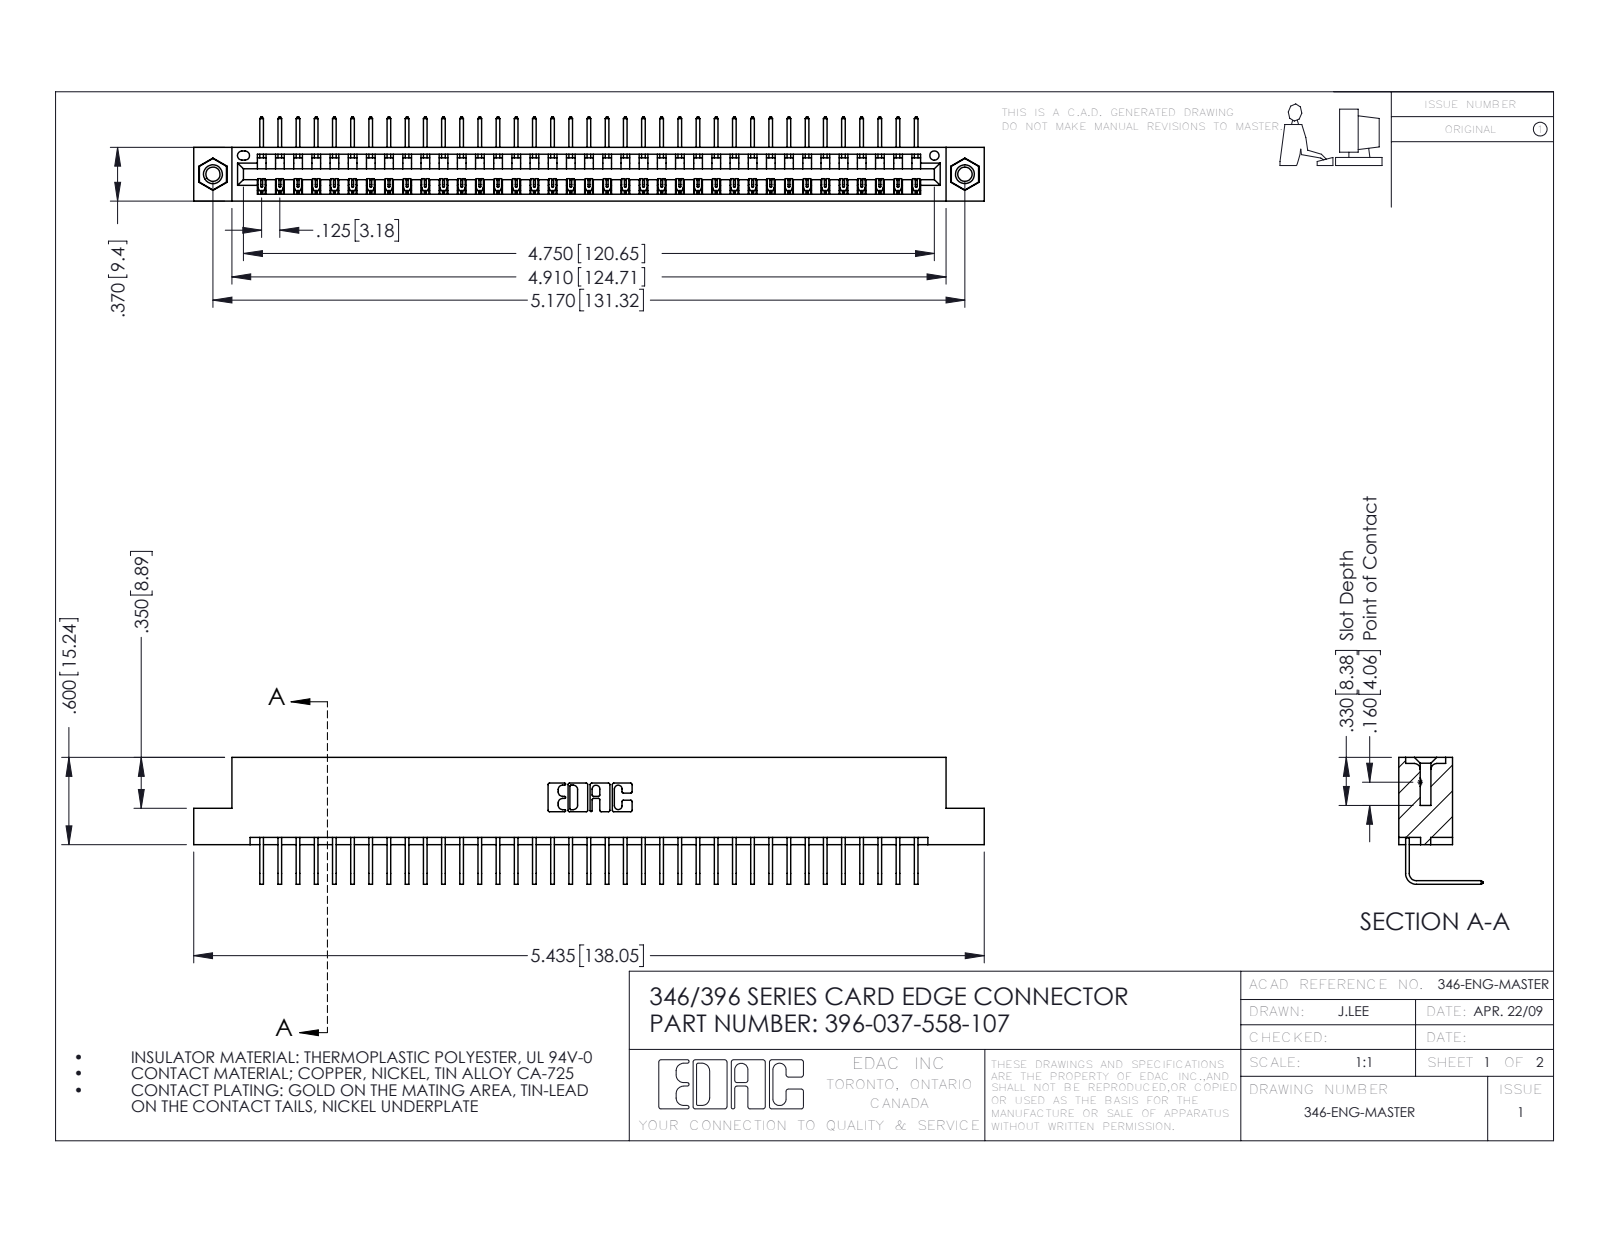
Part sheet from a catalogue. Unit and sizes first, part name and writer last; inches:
Units: inches
Overall size (bounding box): 5.435 × 0.873 × 0.58
Round holes (diameter × count): ⌀0.098 ×2, ⌀0.125 ×2, ⌀0.156 ×2, ⌀0.064 ×1
Round bosses / shafts (diameter × count): ⌀0.155 ×2
Partial cylindrical surfaces — rounded edges, fillets, slot ends (radius × count): R0.006 ×74, R0.01 ×22, R0.007 ×6, R0.031 ×6, R0.026 ×3, R0.031 ×2, R0.04 ×2, R0.014 ×1
Main face-to-face distances: 0.322, 0.048, 0.37, 0.25, 0.298, 0.025, 0.072, 0.148, 0.222, 0.1
Hole centre spacings: 0.246, 4.961, 5.17
Volume: 0.811 in³ · Surface area: 26.86 in²
Bodies: 40 solids, 2402 faces (1662 planar, 724 cylindrical, 16 other)
Part name (STEP PRODUCT): 396-037-558-107; 345-292-001_558 Tail - 2; 345-250-001_345-250-005-103; 346 Part_Flush Mounting Lugs - 0.156 Dia-TI
STEP written by: SolidWorks 2016 (CONFIG_CONTROL_DESIGN)
